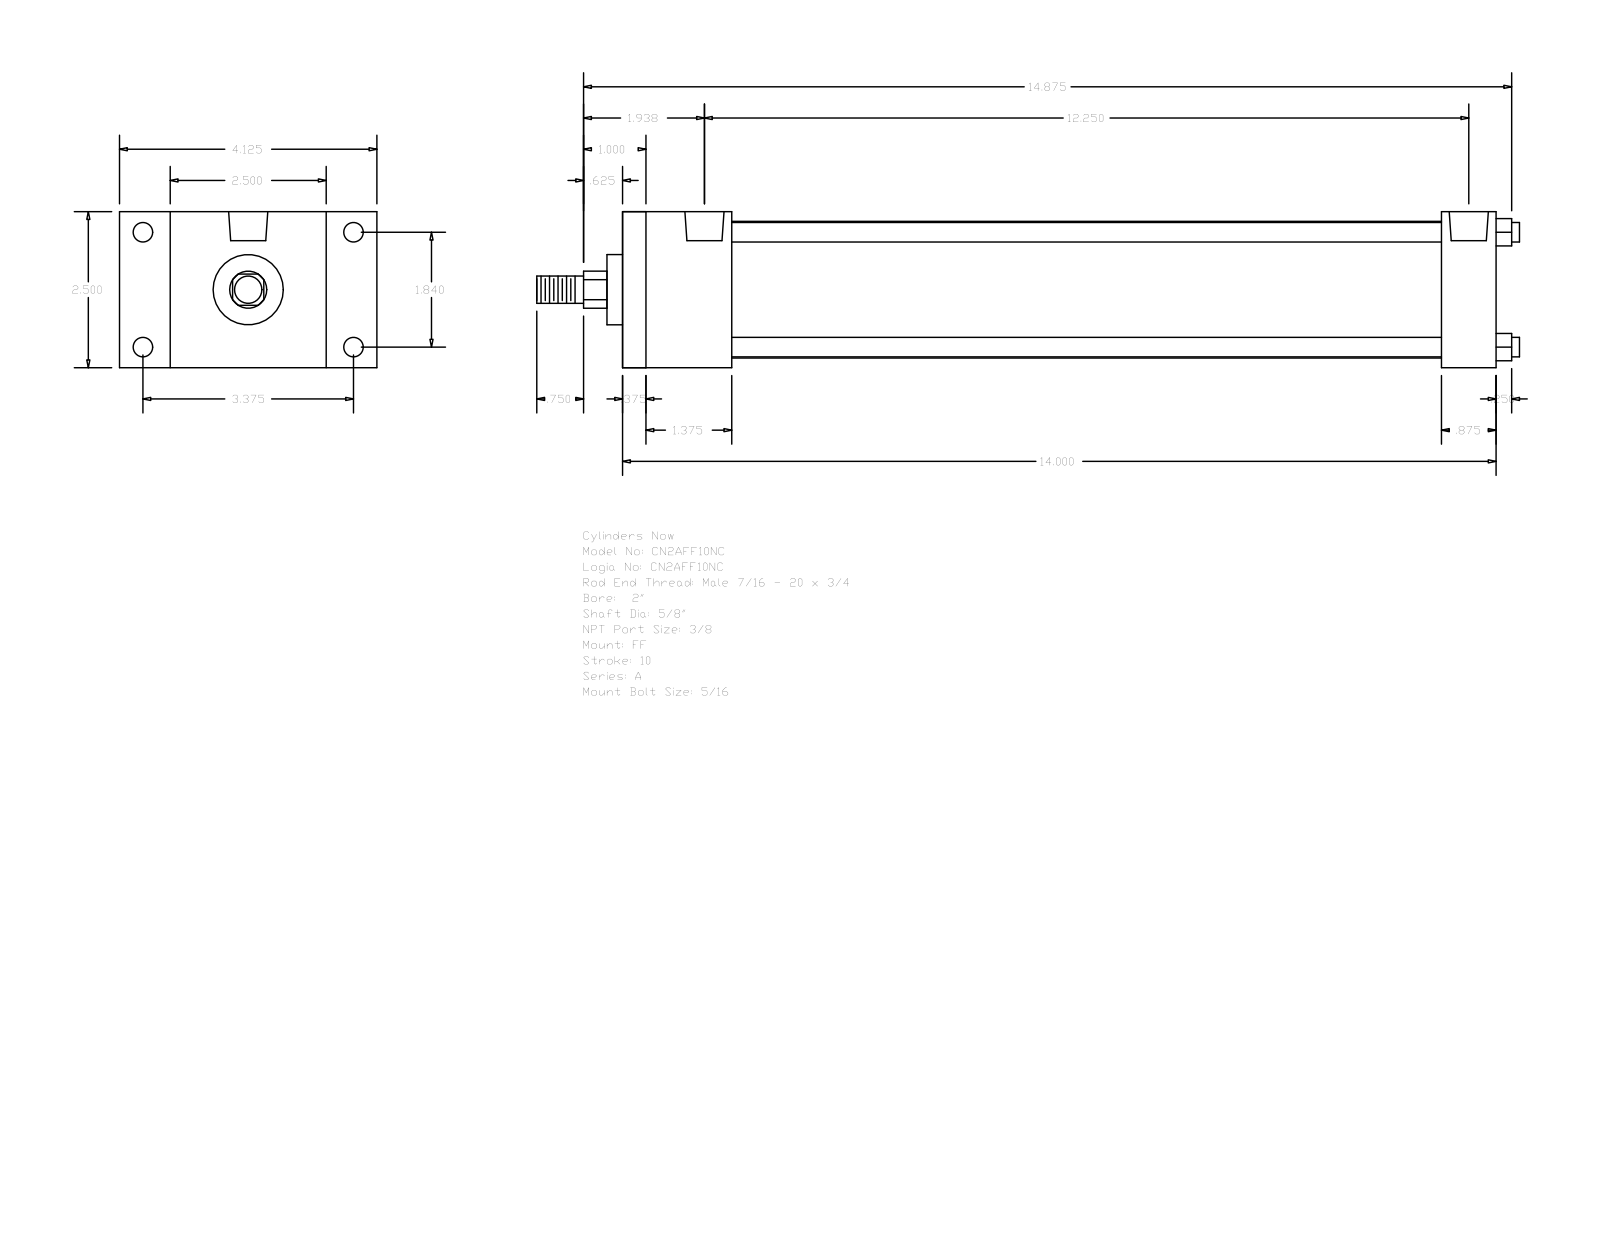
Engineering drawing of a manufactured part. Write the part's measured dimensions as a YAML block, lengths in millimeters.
part_name: "A_FF__0200_0.625"
step_written_by: "GSSL Pune (CONFIG_CONTROL_DESIGN)"
units: millimeters
bodies: {solids: 0, faces: 92, planar: 64, cylindrical: 28, other: 0}
overall_size: [400.05, 104.78, 63.5]
round_holes:
  - {diameter: 5.56, count: 4}
  - {diameter: 7.94, count: 4}
  - {diameter: 15.93, count: 2}
round_bosses_or_shafts:
  - {diameter: 7.94, count: 4}
  - {diameter: 55.63, count: 1}
  - {diameter: 28.57, count: 1}
  - {diameter: 15.88, count: 1}
  - {diameter: 11.11, count: 1}
partial_cylinders:
  - {radius: 7.54, count: 1}
face_to_face_distances: [63.5, 355.6, 9.52, 346.08, 34.93, 44.45, 333.37, 323.85, 288.92, 311.15]
hole_center_spacings: [46.74, 85.72, 97.63, 303.2, 3.97, 3.98, 307.17, 307.18]
